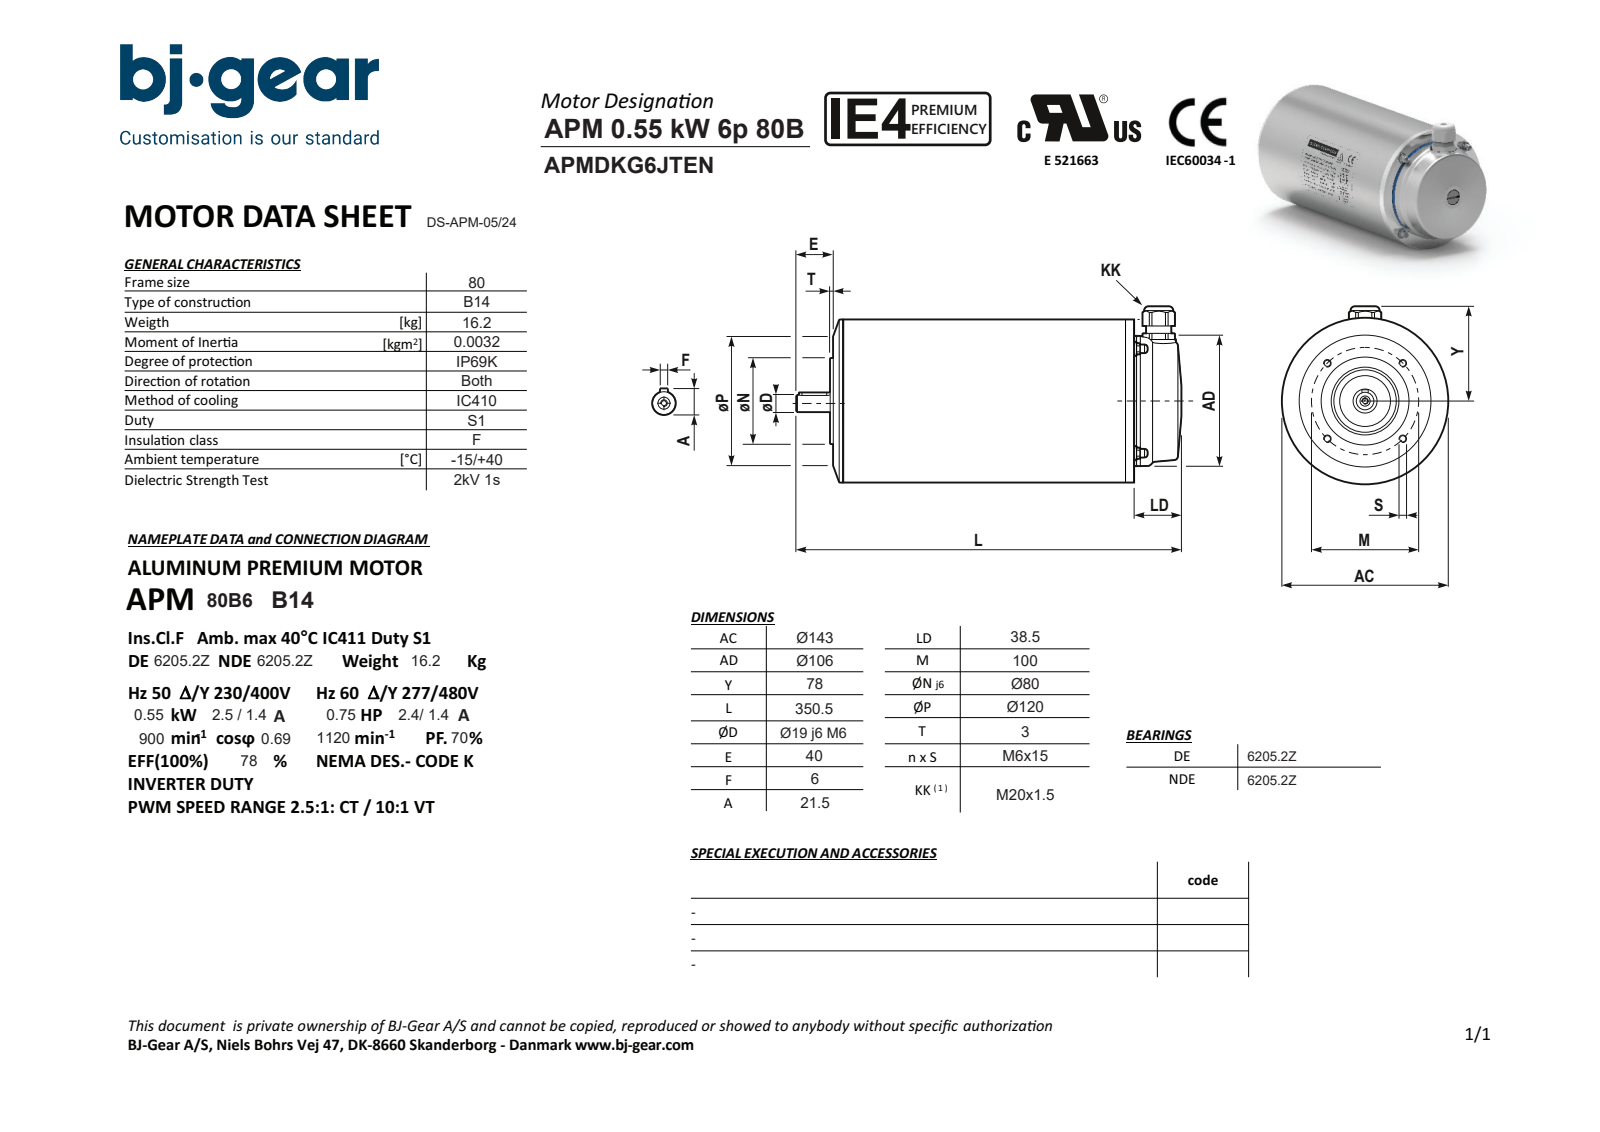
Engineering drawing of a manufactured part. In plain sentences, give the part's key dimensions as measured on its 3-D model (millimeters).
The part is named "APMDKG6JTENN4KCR2-N---NNN". Its 3-D file was written by "Solid Edge (AUTOMOTIVE_DESIGN)". It is 1 solid with 156 faces: 75 planar, 50 cylindrical and 31 other. Overall it measures 350.5 by 148.3 by 142.6 millimeters. Its volume is 4 636 000 cubic millimeters and its surface area 172 344 square millimeters. Round holes: 5 of diameter 4.92, 1 of diameter 6.4, 1 of diameter 16, 1 of diameter 28, 1 of diameter 65. Round bosses or shafts: 4 of diameter 11.5, 4 of diameter 7, 1 of diameter 142.6, 1 of diameter 142.6, 1 of diameter 106, 1 of diameter 80, 1 of diameter 25, 1 of diameter 23.7. Partial cylindrical surfaces (rounded edges, fillets, slot ends): 2 of radius 3, 1 of radius 13.2. The main face-to-face distances are 272, 6, 266, 9, 3, 275, 24, 310.5, 38.5, 304.5. The hole center spacings are 50.01, 70.72, 100.01.
